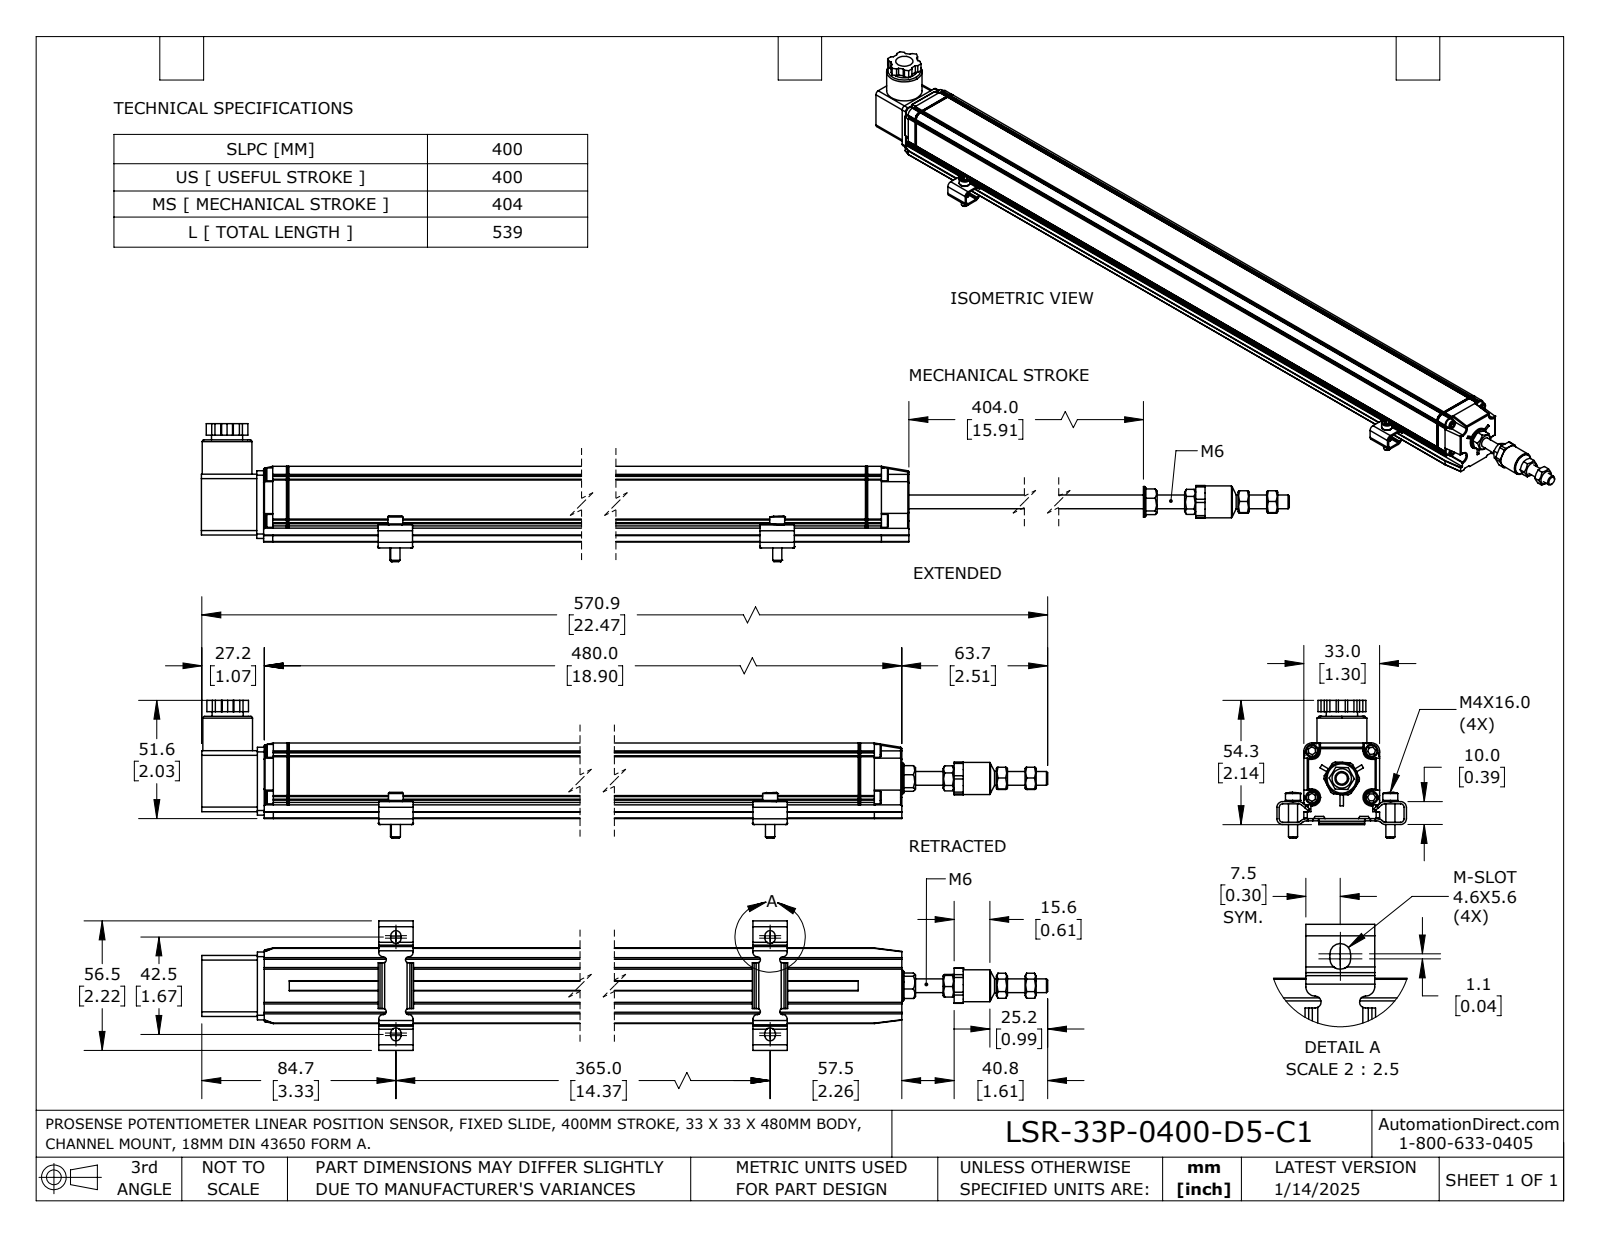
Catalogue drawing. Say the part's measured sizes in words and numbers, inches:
The part is named "LSR-33P-0400-D5-C1". Its 3-D file was written by "SolidWorks 2023 (AUTOMOTIVE_DESIGN)". It is 14 solids with 995 faces: 641 planar, 269 cylindrical and 85 other. Overall it measures 22.474 by 2.37 by 2.224 inches. Its volume is 29.9 cubic inches and its surface area 193.6 square inches. Round holes: 4 of diameter 0.106, 4 of diameter 0.13, 1 of diameter 0.169, 1 of diameter 0.205, 1 of diameter 0.209, 1 of diameter 0.232, 1 of diameter 0.276, 1 of diameter 0.285, 1 of diameter 0.394, 1 of diameter 0.413, 1 of diameter 0.573, 1 of diameter 0.602. Round bosses or shafts: 5 of diameter 0.157, 5 of diameter 0.118, 4 of diameter 0.256, 4 of diameter 0.22, 1 of diameter 0.854, 1 of diameter 0.551, 1 of diameter 0.535, 1 of diameter 0.528. Partial cylindrical surfaces (rounded edges, fillets, slot ends): 28 of radius 0.079, 23 of radius 0.02, 16 of radius 0.008, 8 of radius 0.051, 8 of radius 0.059, 8 of radius 0.089, 8 of radius 0.118, 4 of radius 0.039. The main face-to-face distances are 1.299, 0.118, 0.22, 1.181, 0.039, 1.079, 0.079, 0.142, 0.102, 0.185. The hole center spacings are 0.047, 0.583, 0.607, 0.696, 0.73, 0.799, 1.024, 1.299.
